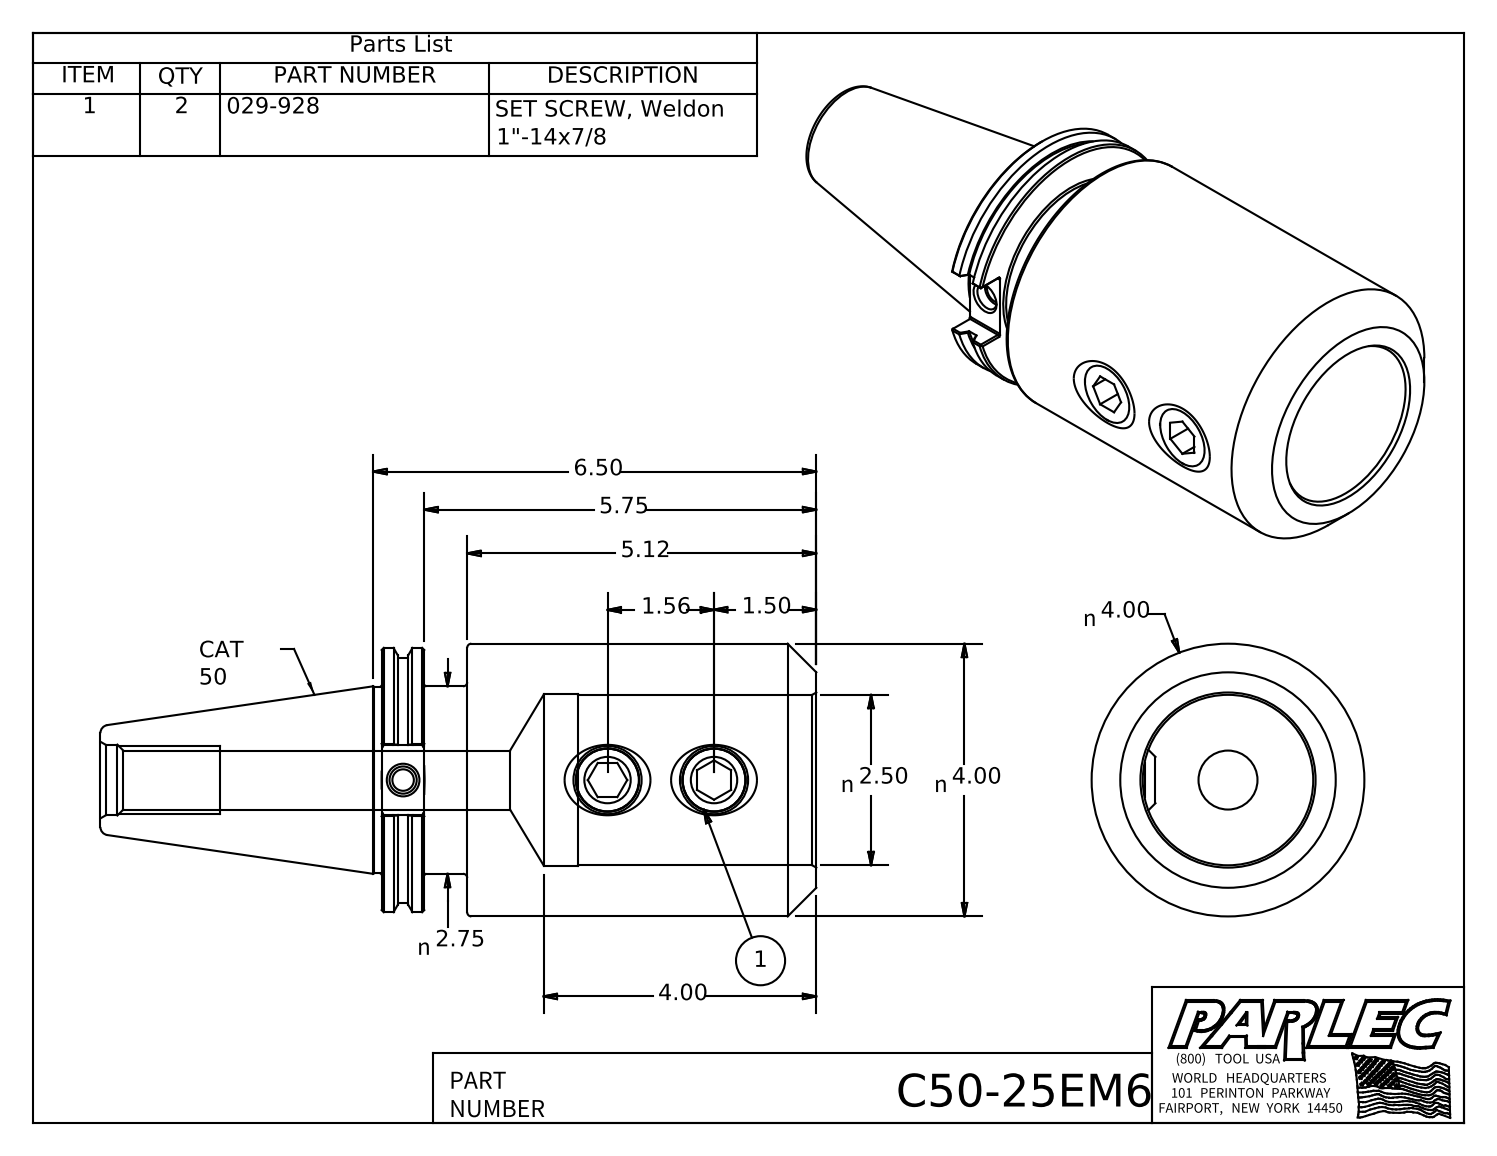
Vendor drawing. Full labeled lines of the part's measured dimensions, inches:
Part name (STEP PRODUCT): C50-25EM6; C50-25EM6-1; 029-928
STEP written by: Autodesk Inventor 2012 (AUTOMOTIVE_DESIGN)
Units: inches
Bodies: 3 solids, 119 faces (52 planar, 31 cylindrical, 36 other)
Overall size (bounding box): 10.5 × 4 × 4
Volume: 64.84 in³ · Surface area: 193.7 in²
Round holes (diameter × count): ⌀0.923 ×2, ⌀0.315 ×1, ⌀0.399 ×1, ⌀0.865 ×1, ⌀1.038 ×1, ⌀2.5 ×1, ⌀2.53 ×1
Round bosses / shafts (diameter × count): ⌀1 ×2, ⌀4 ×1, ⌀3.875 ×1, ⌀3.594 ×1, ⌀2.75 ×1, ⌀2.73 ×1
Partial cylindrical surfaces — rounded edges, fillets, slot ends (radius × count): R0.02 ×12
Main face-to-face distances: 1.255, 0.625, 0.63, 6.375, 5.75, 5.12, 0.5, 0.875, 2.452, 3.327
Hole centre spacings: 1.562, 2.998, 4.56
